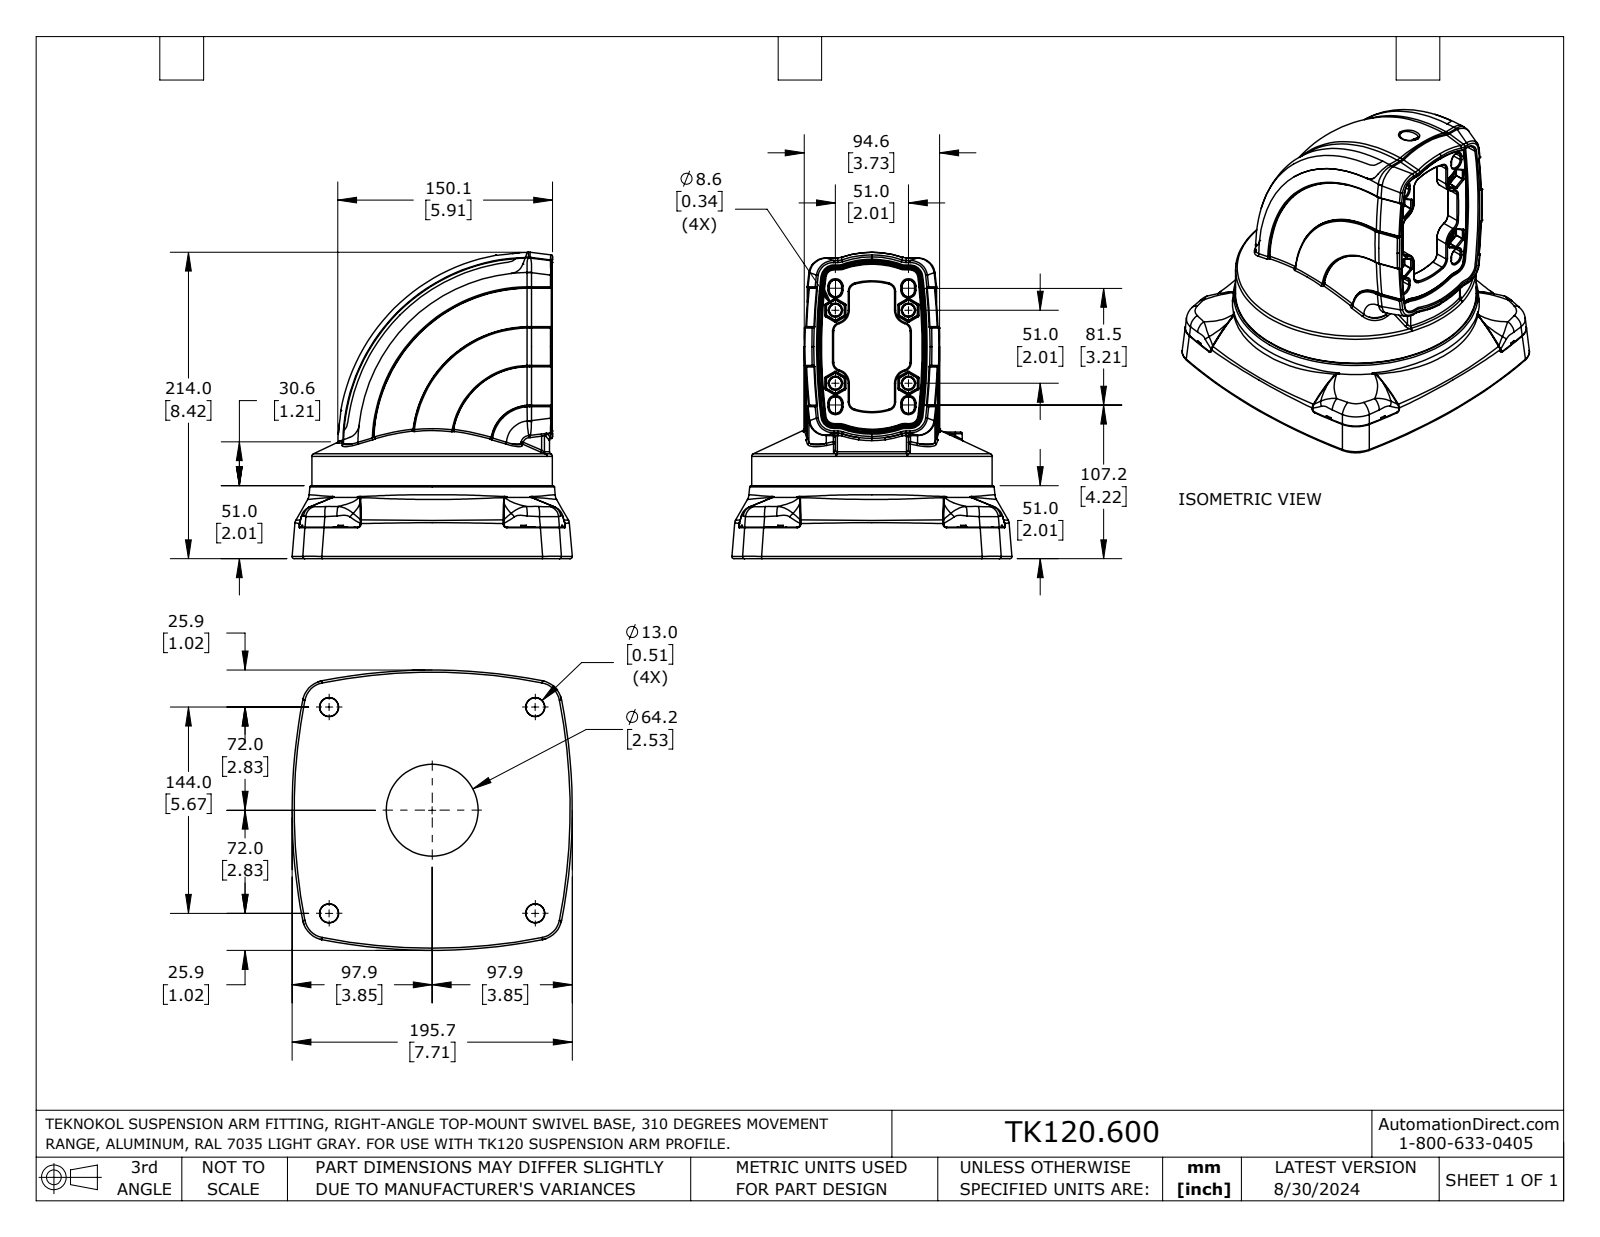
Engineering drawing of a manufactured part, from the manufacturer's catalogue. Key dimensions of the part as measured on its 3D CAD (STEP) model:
Part name (STEP PRODUCT): TK120.600_REV2
STEP written by: SolidWorks 2023 (AUTOMOTIVE_DESIGN)
Units: inches
Bodies: 1 solid, 1216 faces (161 planar, 189 cylindrical, 866 other)
Overall size (bounding box): 8.424 × 7.706 × 7.706
Volume: 207.7 in³ · Surface area: 289.5 in²
Round holes (diameter × count): ⌀0.197 ×1
Round bosses / shafts (diameter × count): ⌀0.197 ×8, ⌀0.394 ×2, ⌀6.614 ×1, ⌀0.236 ×1
Partial cylindrical surfaces — rounded edges, fillets, slot ends (radius × count): R0.01 ×44, R0.029 ×26, R0.004 ×12, R0.108 ×12, R0.079 ×10, R0.077 ×8, R0.209 ×8, R0.055 ×4
Main face-to-face distances: 0.383, 0.866, 0.098, 0.768, 0.129, 0.512, 2.008, 1.004, 0.03, 0.482
